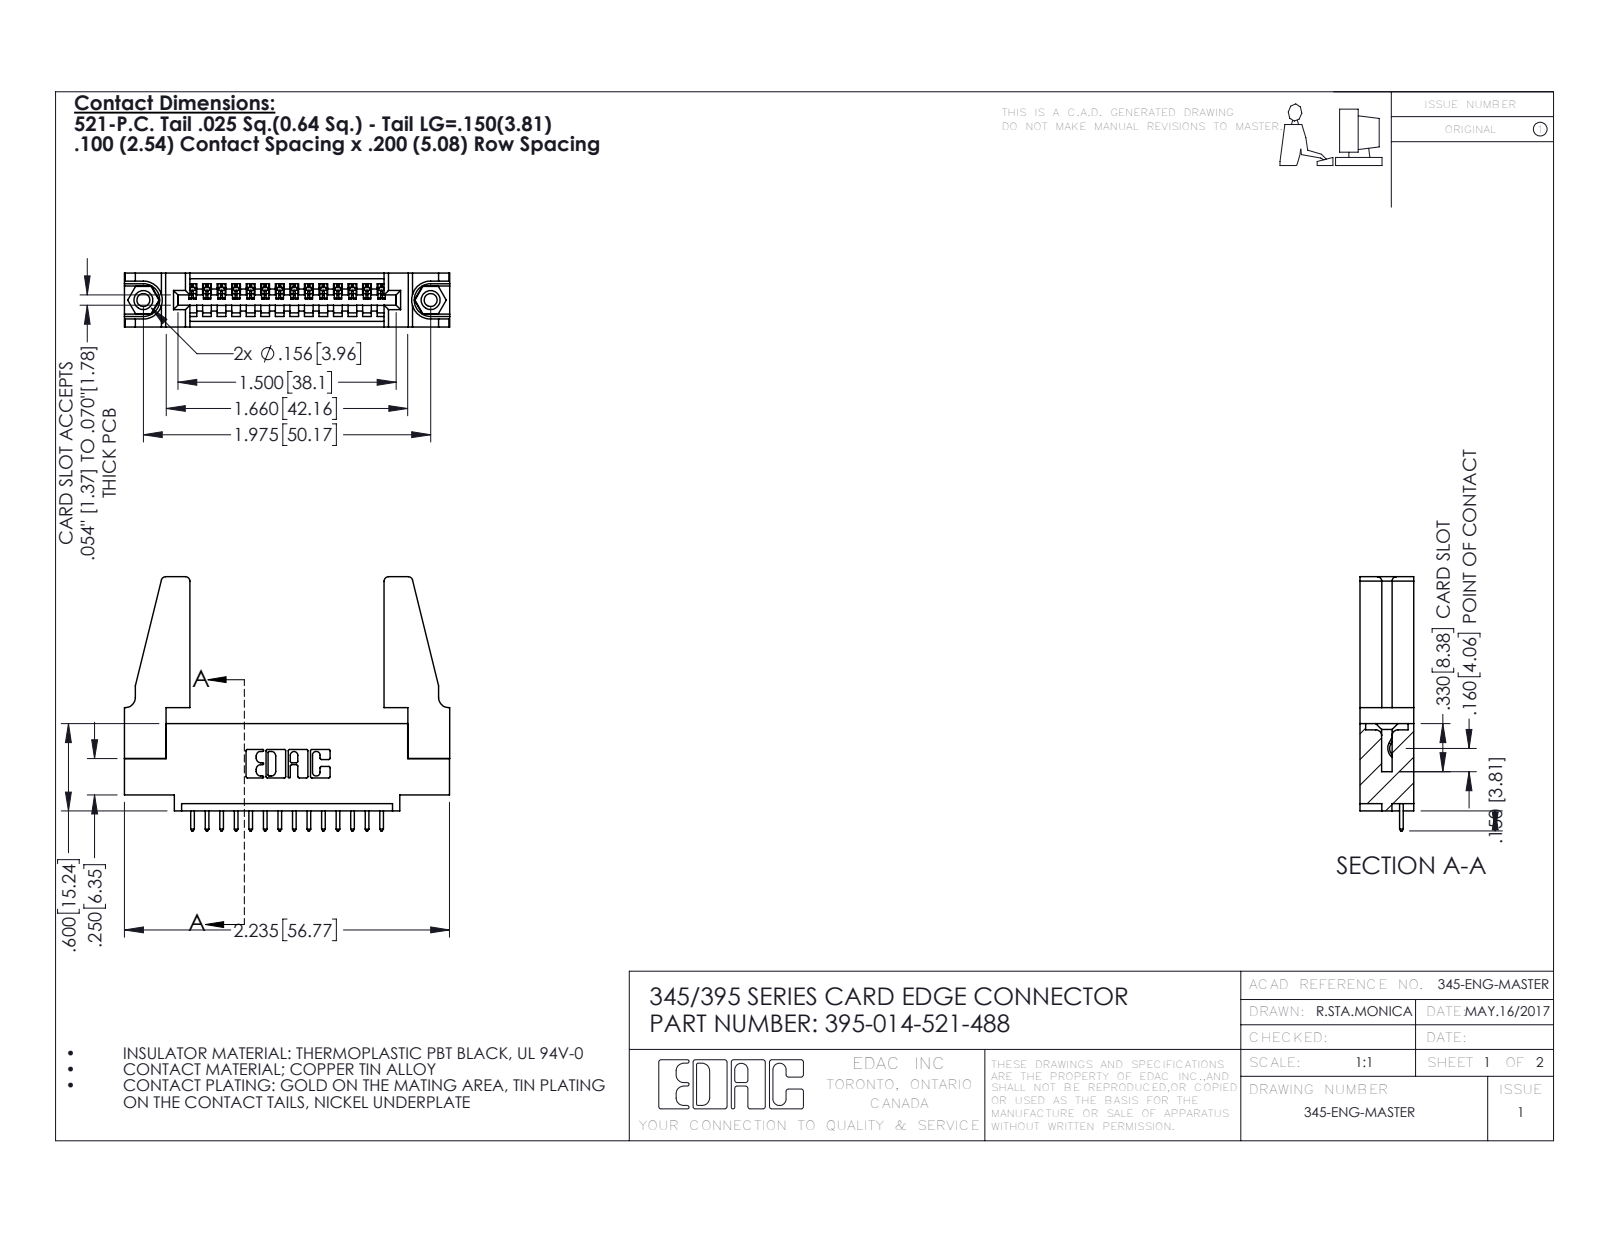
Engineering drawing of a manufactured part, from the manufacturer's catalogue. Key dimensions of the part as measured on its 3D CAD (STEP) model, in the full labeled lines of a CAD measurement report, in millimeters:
Part name (STEP PRODUCT): 345-250-001_345-250-001-102; 345-220-078_345-220-088; 345 Part_0.110 Offset - 0.156 Dia-TH; 395-014-521-488 (+1 more)
STEP written by: SolidWorks 2016 (CONFIG_CONTROL_DESIGN)
Units: millimetres
Bodies: 19 solids, 1066 faces (716 planar, 334 cylindrical, 16 other)
Overall size (bounding box): 56.8 × 44.4 × 9.4
Volume: 8 310 mm³ · Surface area: 9 387 mm²
Round holes (diameter × count): ⌀2.3 ×2, ⌀3.2 ×2, ⌀4 ×2, ⌀1.6 ×1
Round bosses / shafts (diameter × count): ⌀3.9 ×2
Partial cylindrical surfaces — rounded edges, fillets, slot ends (radius × count): R0.2 ×28, R0.3 ×28, R0.3 ×22, R0.8 ×8, R0.2 ×6, R0.8 ×6, R0.7 ×3, R0.8 ×2
Main face-to-face distances: 9.4, 1.8, 7.6, 5.1, 2.5, 6.9, 0.6, 5.7, 3.8, 3.8
Hole centre spacings: 6.9, 44.2, 50.2
